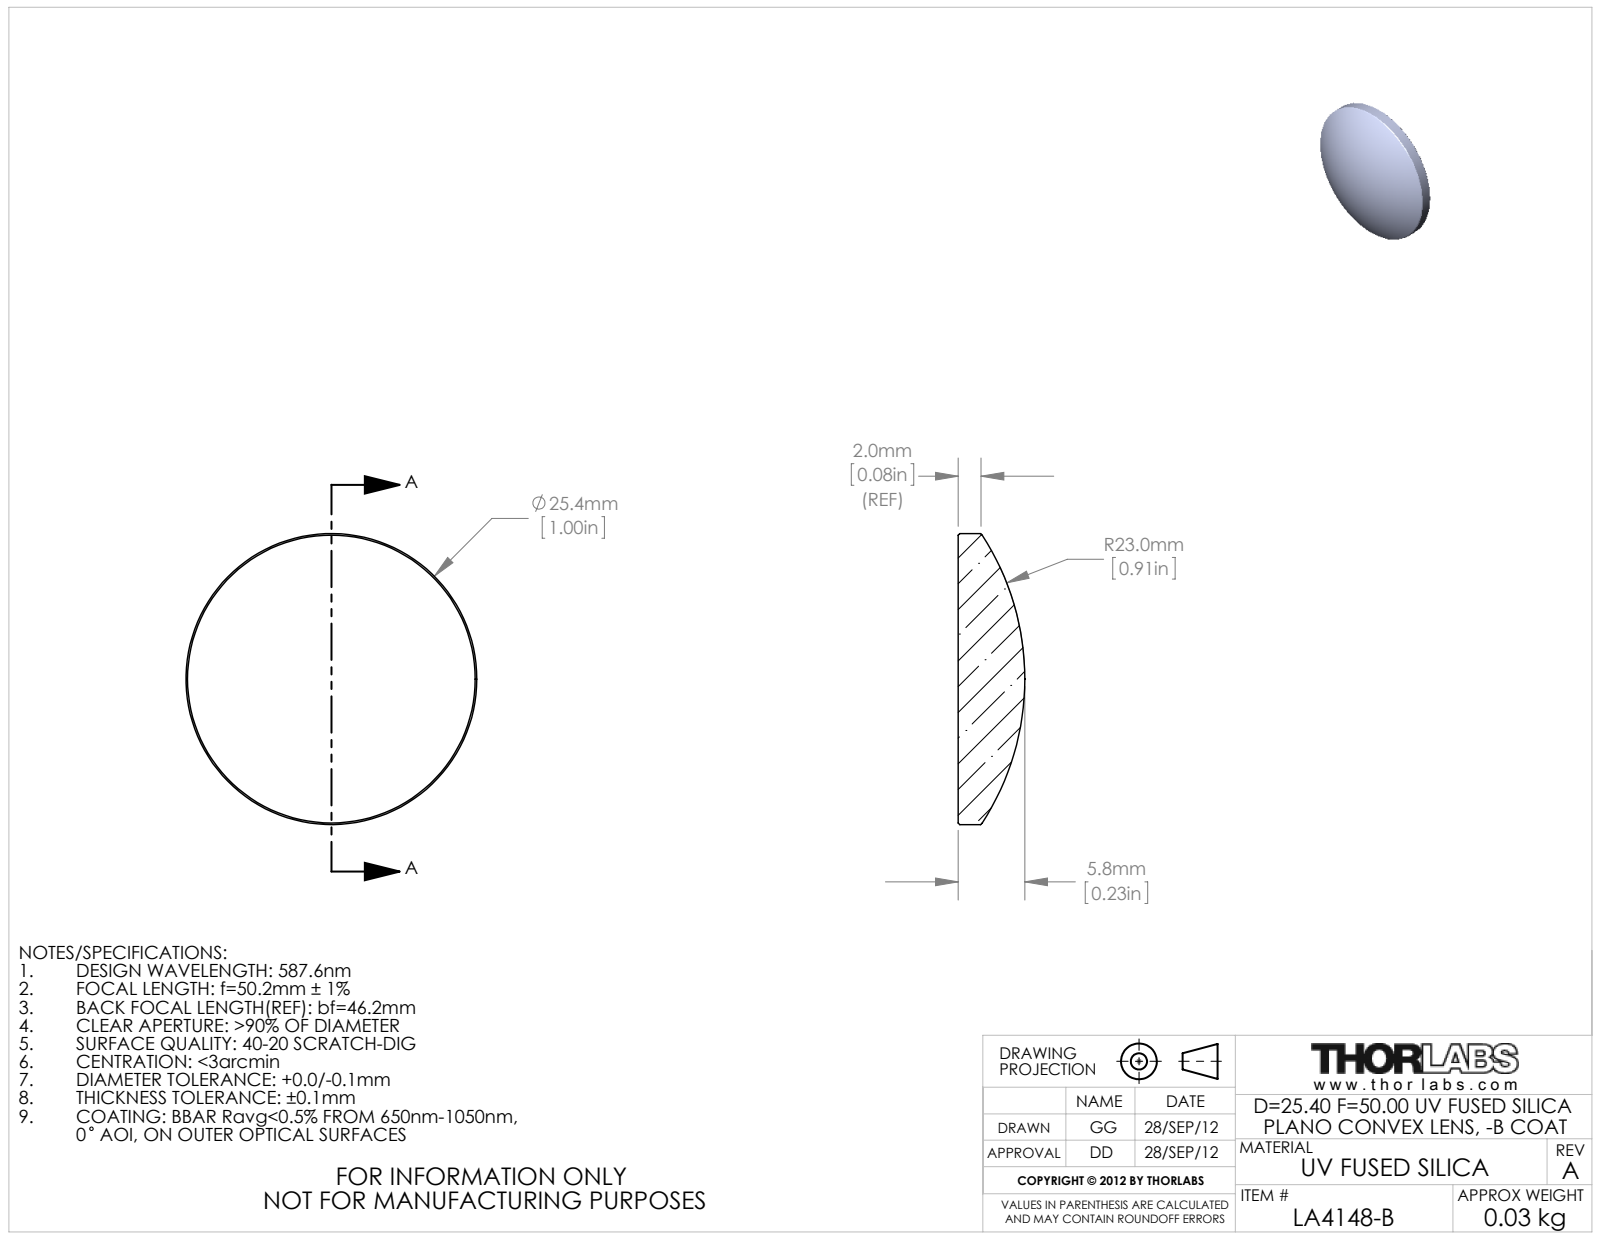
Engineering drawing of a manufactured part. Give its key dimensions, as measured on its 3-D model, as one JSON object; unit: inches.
{"part_name": "24973-E0W", "step_written_by": "SolidWorks 2011 (CONFIG_CONTROL_DESIGN)", "units": "inches", "bodies": {"solids": 1, "faces": 9, "planar": 1, "cylindrical": 2, "other": 6}, "overall_size": [1, 1, 0.229], "volume_in3": 0.123, "surface_area_in2": 1.877, "round_bosses_or_shafts": [[1, 1]]}
